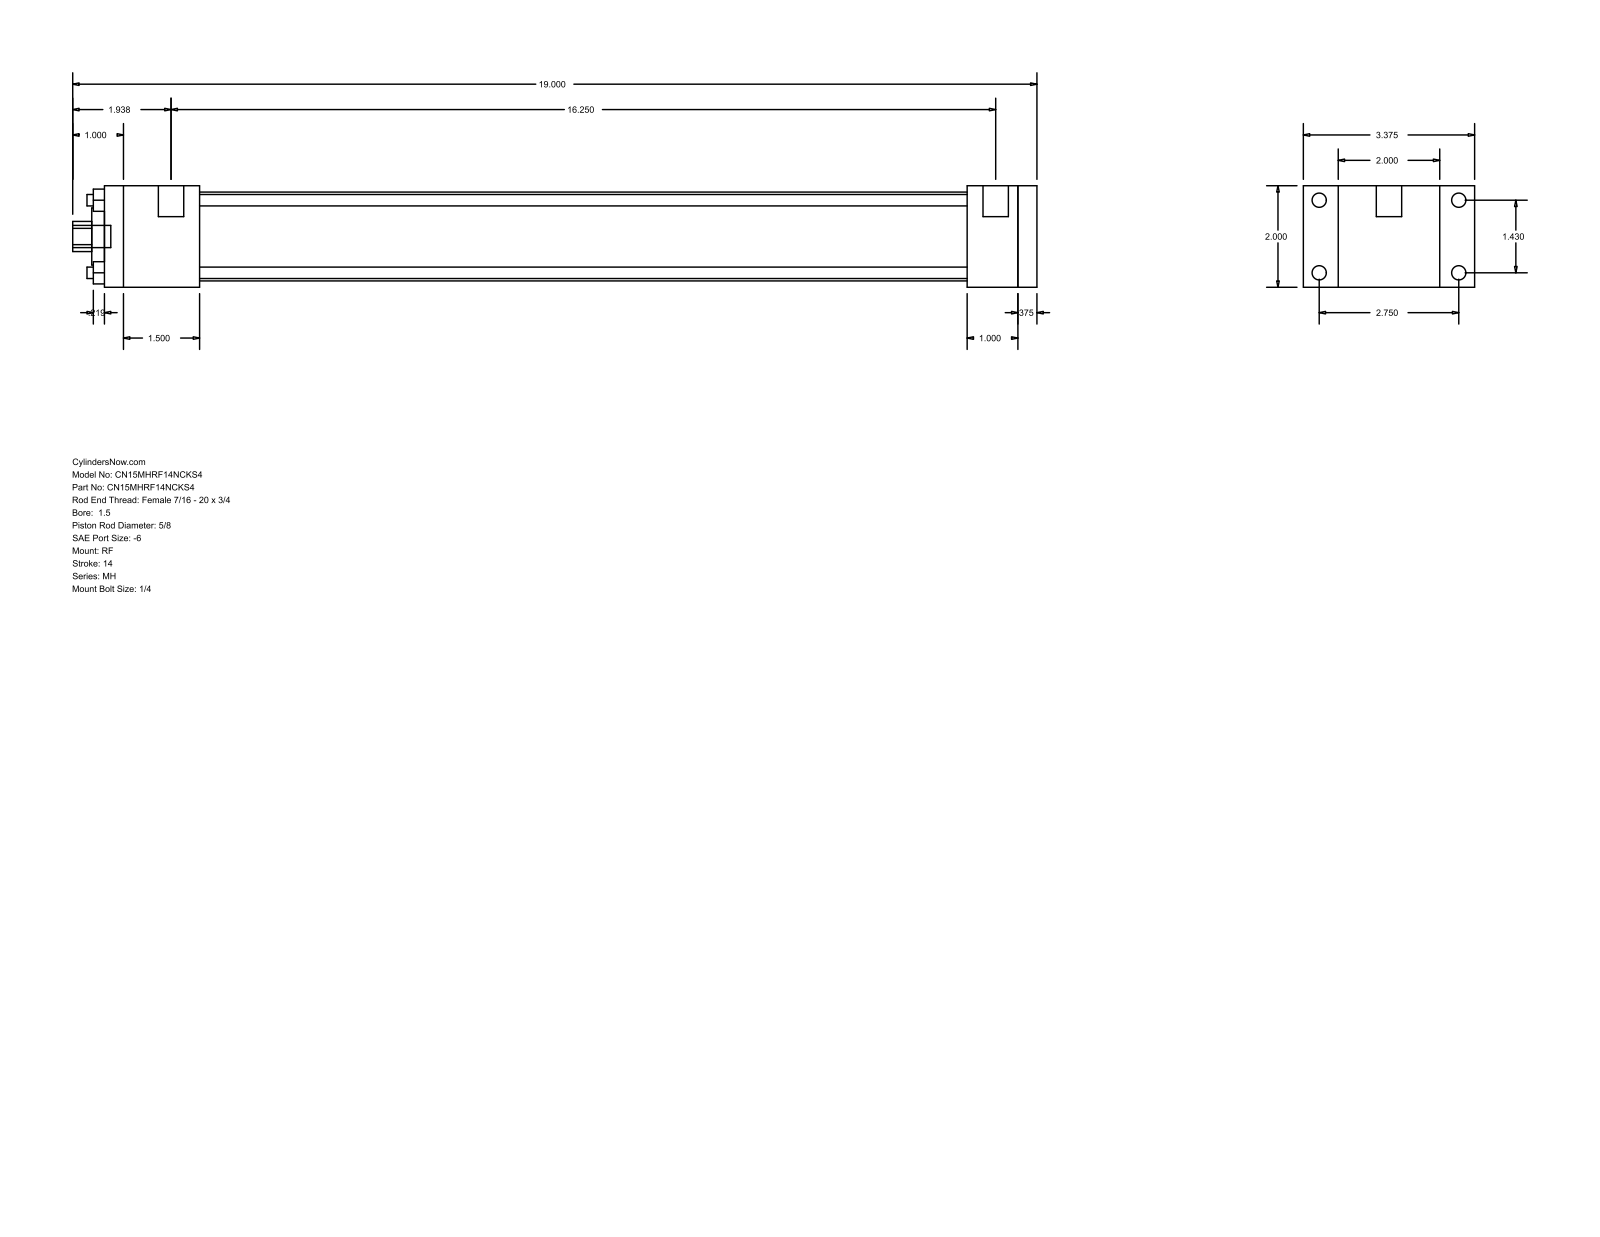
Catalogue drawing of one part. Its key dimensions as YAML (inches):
part_name: "MH_RF__0150_0.625"
step_written_by: "GSSL Pune (CONFIG_CONTROL_DESIGN)"
units: inches
bodies: {solids: 0, faces: 92, planar: 64, cylindrical: 28, other: 0}
overall_size: [19, 3.375, 2]
round_holes:
  - {diameter: 0.225, count: 4}
  - {diameter: 0.625, count: 1}
  - {diameter: 1.125, count: 1}
  - {diameter: 1.75, count: 1}
round_bosses_or_shafts:
  - {diameter: 0.281, count: 4}
  - {diameter: 0.219, count: 4}
  - {diameter: 0.5, count: 2}
  - {diameter: 0.437, count: 1}
partial_cylinders:
  - {radius: 0.297, count: 1}
face_to_face_distances: [2, 0.375, 18.375, 18, 0.687, 2.687, 17, 1, 1.375, 1.875]
hole_center_spacings: [1.011, 1.43, 2.022]
